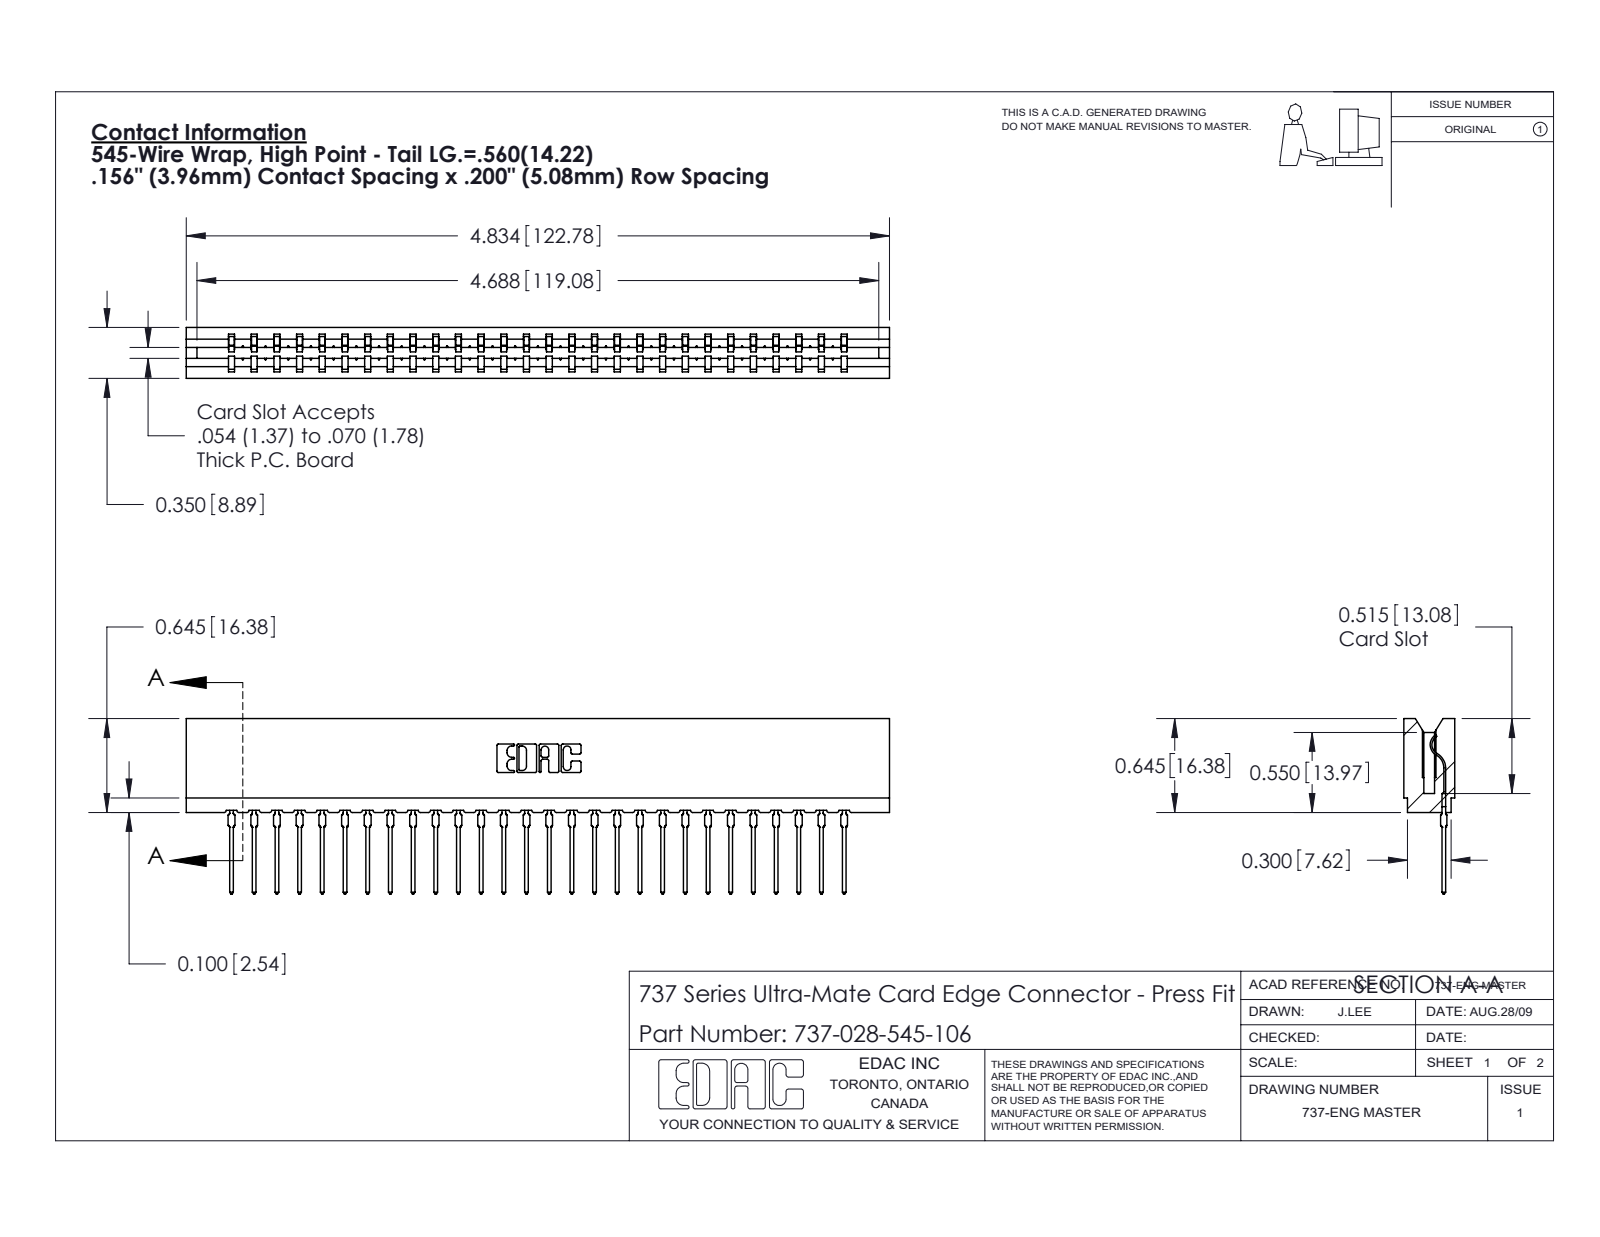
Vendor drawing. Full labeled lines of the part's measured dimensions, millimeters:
Part name (STEP PRODUCT): 737-028-545-106; 737 Part_Insulator Option - 06; 745-292-001_545
STEP written by: SolidWorks 2020 (CONFIG_CONTROL_DESIGN)
Units: millimetres
Bodies: 29 solids, 3259 faces (1959 planar, 572 cylindrical, 728 other)
Overall size (bounding box): 122.8 × 30.6 × 8.9
Volume: 12 000 mm³ · Surface area: 16 360 mm²
Partial cylindrical surfaces — rounded edges, fillets, slot ends (radius × count): R0.4 ×56, R0.5 ×56, R0.3 ×22, R0.2 ×6, R0.8 ×6, R0.1 ×4, R0.3 ×4, R0.7 ×3
Main face-to-face distances: 3.5, 5.4, 8.9, 1.9, 4, 1.1, 7.7, 2.4, 4.2, 1.6
